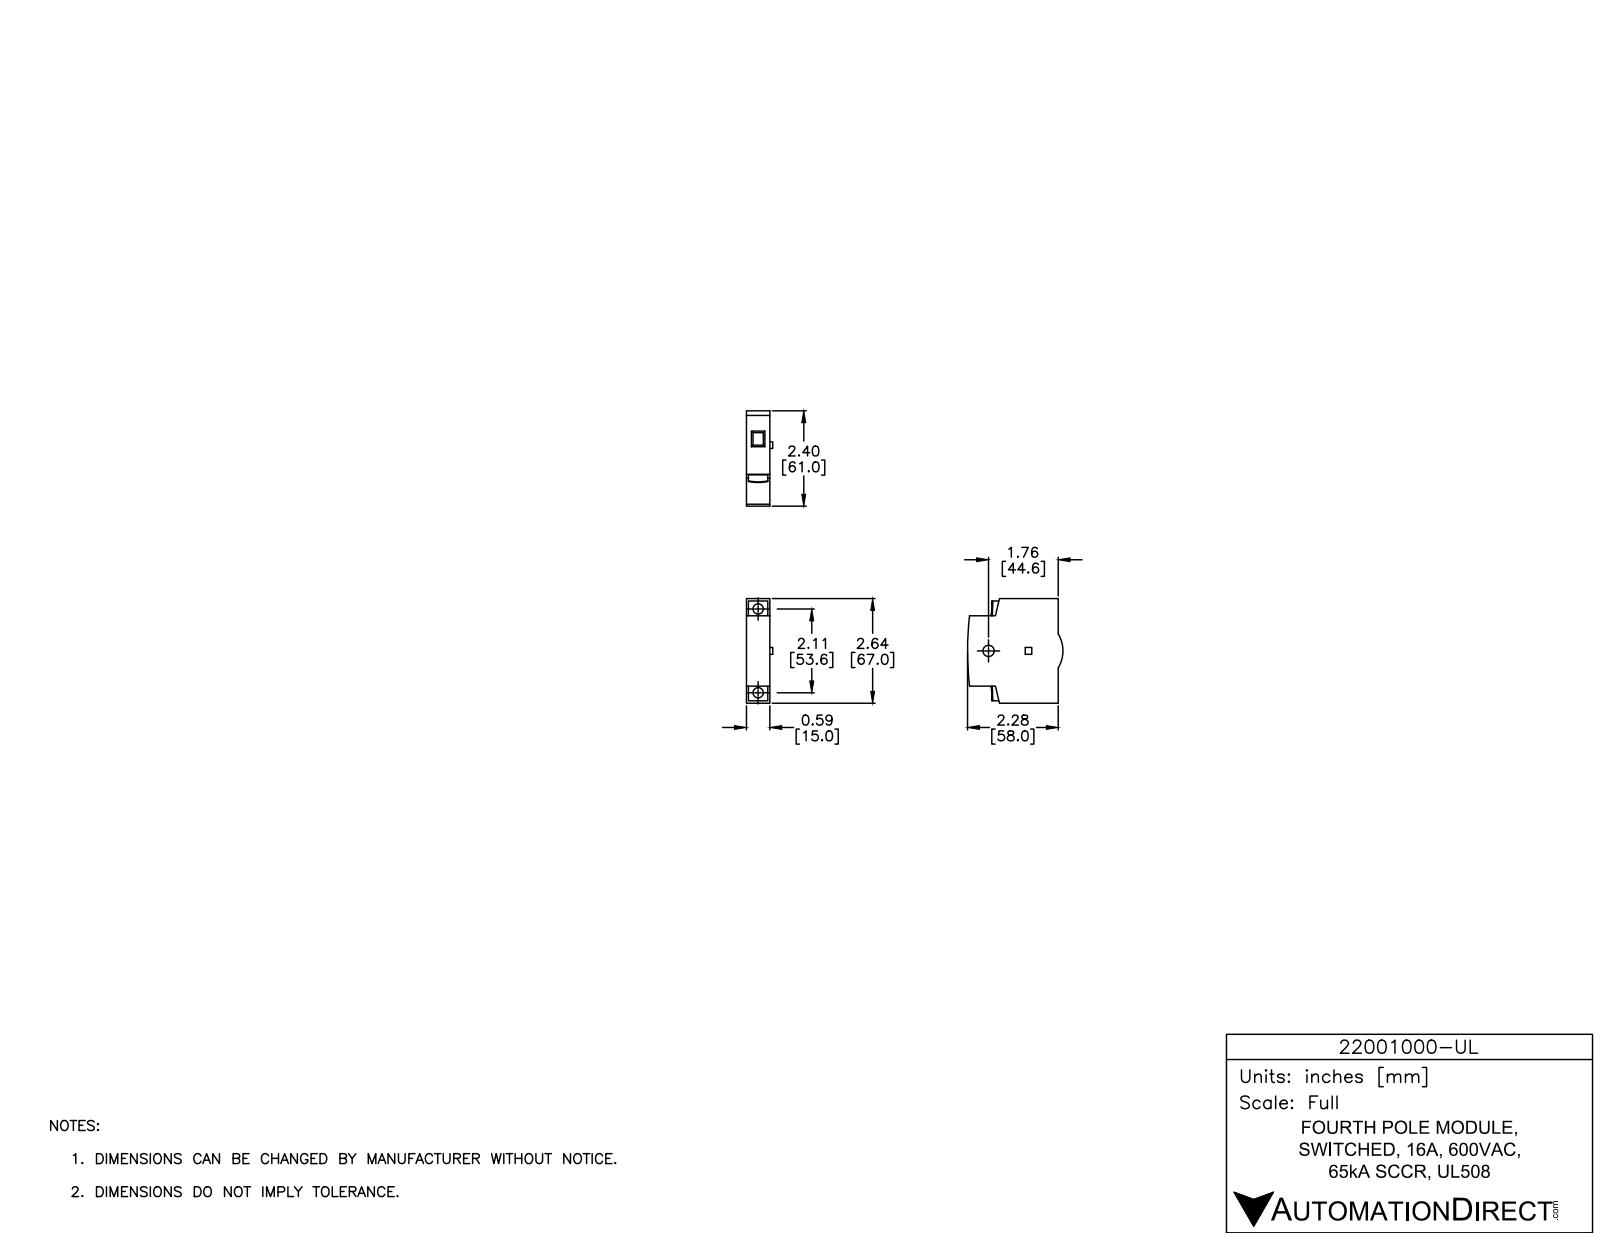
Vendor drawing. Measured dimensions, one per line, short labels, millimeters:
name: 22001000-UL
written by: SolidWorks 2015 (AUTOMOTIVE_DESIGN)
unit: mm
bodies: 1 solid, 61 faces (46 planar, 11 cylindrical, 4 other)
size: 67 × 61 × 16.9
volume: 51 470 mm³; area: 11 700 mm²
holes: 2× ⌀6.6, 1× ⌀7.2
rounds: 1× R21, 1× R200
face distances: 15, 67, 11, 56, 45, 1.6, 65.4, 9.4, 54.4, 1.3
hole spacings: 53.6
